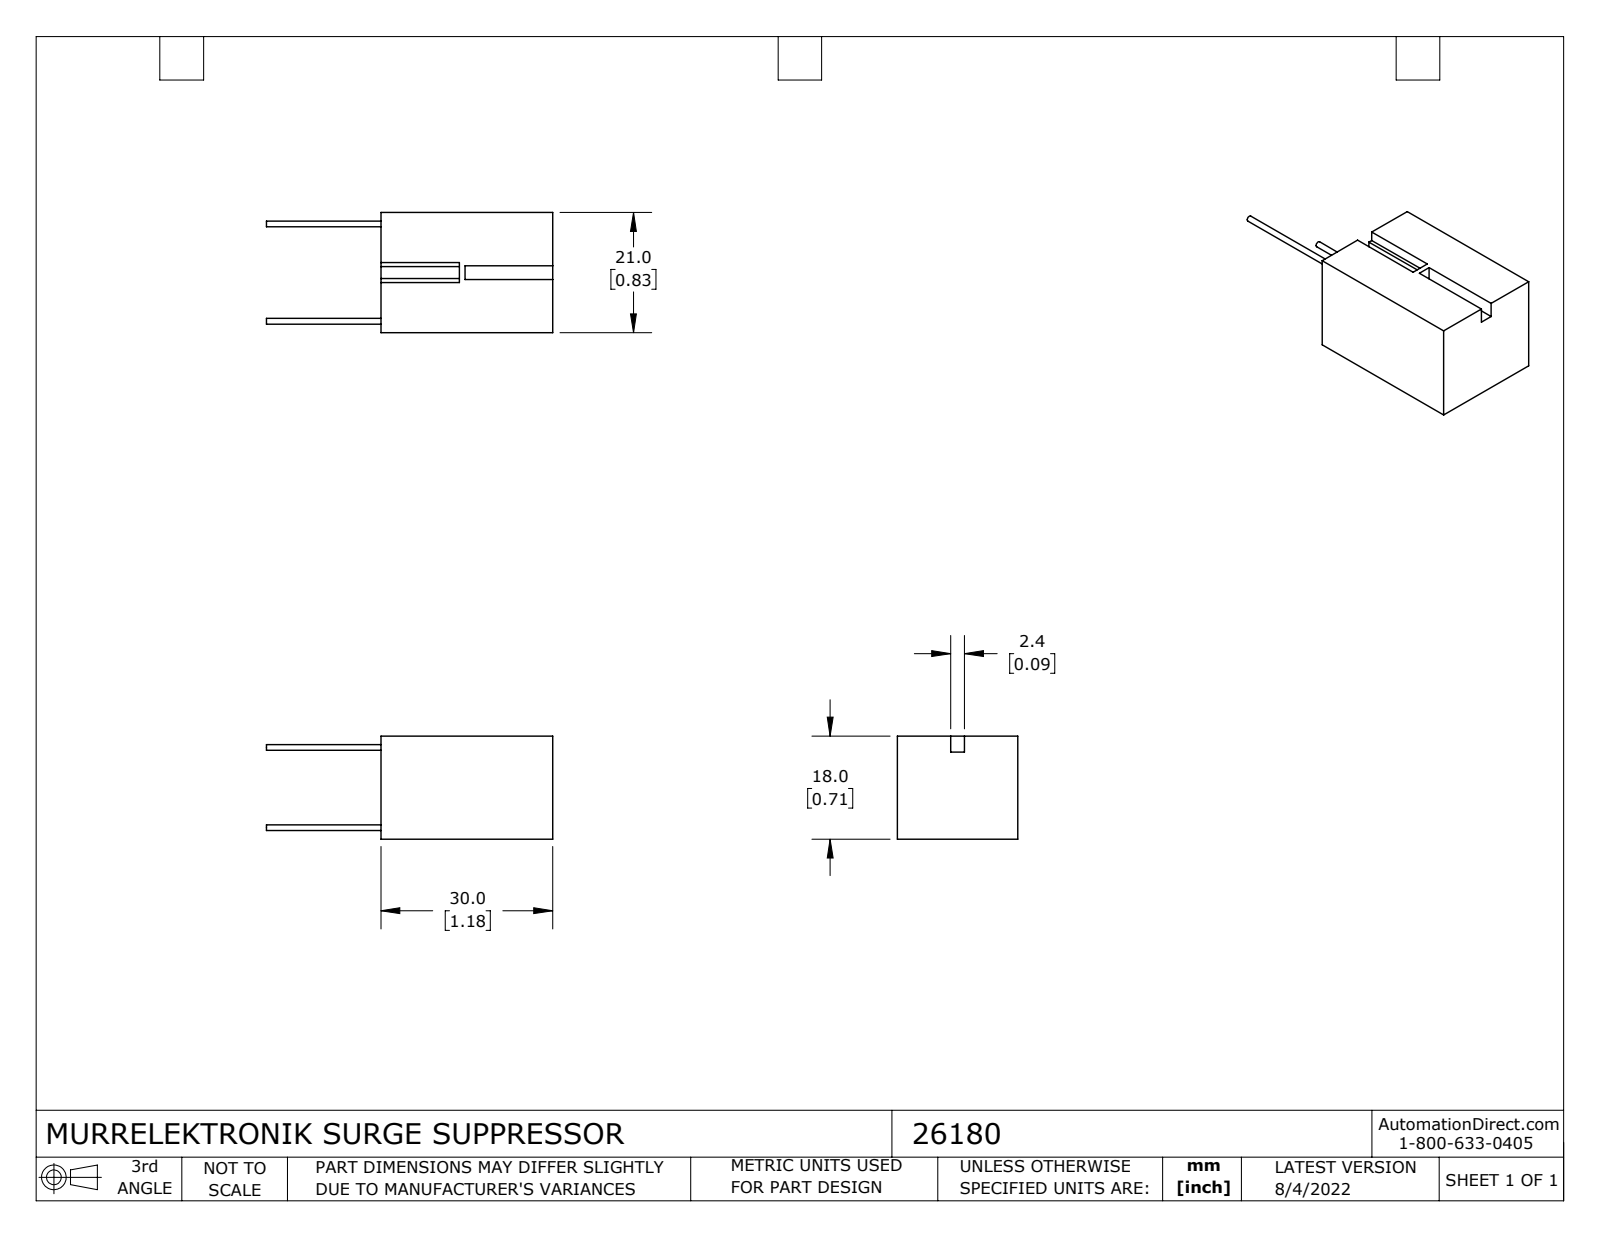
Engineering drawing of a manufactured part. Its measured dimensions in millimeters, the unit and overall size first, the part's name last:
Units: millimetres
Overall size (bounding box): 50 × 21 × 18
Round bosses / shafts (diameter × count): ⌀1 ×2
Main face-to-face distances: 18, 21, 30, 2.8, 9.3, 11.7, 15.2, 8.75, 12.25, 0.55
Volume: 11 154 mm³ · Surface area: 3 384 mm²
Bodies: 1 solid, 24 faces (20 planar, 4 cylindrical, 0 other)
Part name (STEP PRODUCT): 26180
STEP written by: SolidWorks 2021 (CONFIG_CONTROL_DESIGN)
